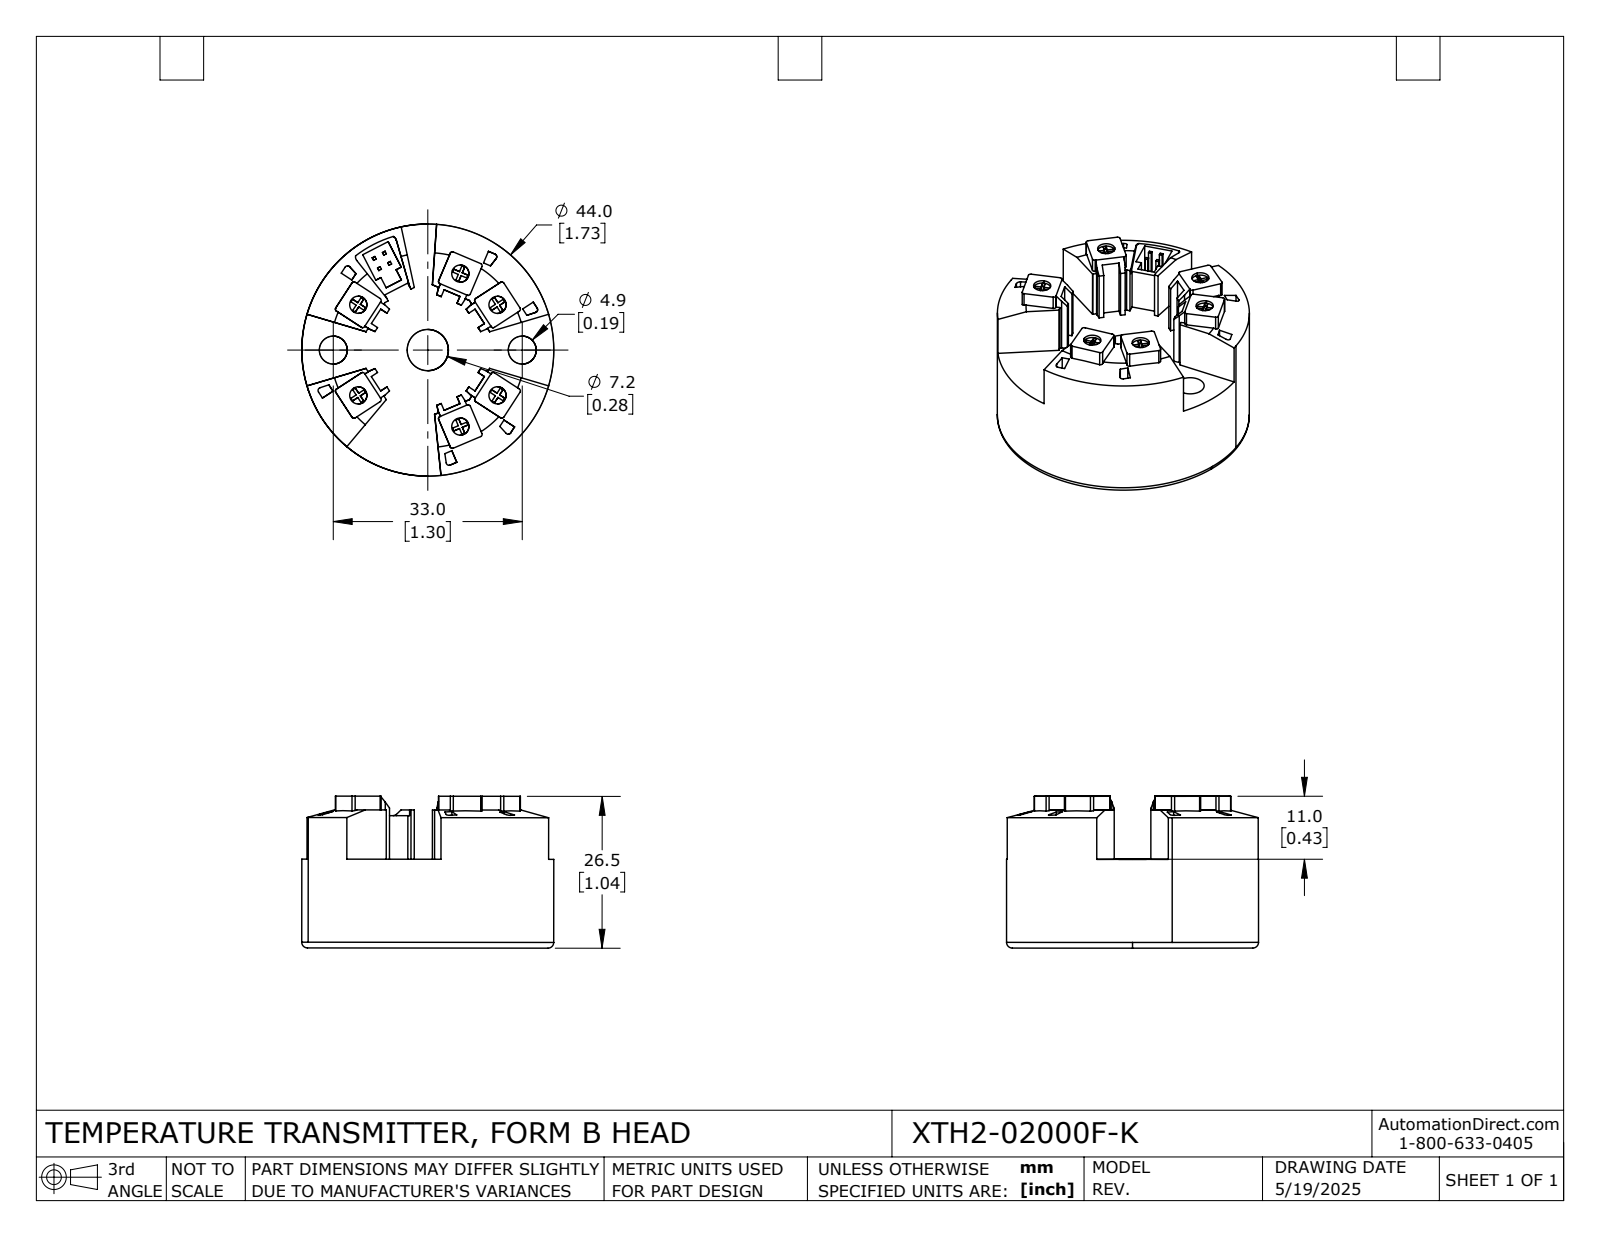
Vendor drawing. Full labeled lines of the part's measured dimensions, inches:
Part name (STEP PRODUCT): XTDH2-02000F-K
STEP written by: SolidWorks 2024 (AUTOMOTIVE_DESIGN)
Units: inches
Bodies: 1 solid, 341 faces (281 planar, 52 cylindrical, 8 other)
Overall size (bounding box): 1.733 × 1.732 × 1.045
Volume: 1.748 in³ · Surface area: 13.46 in²
Round holes (diameter × count): ⌀0.118 ×6, ⌀0.193 ×2, ⌀0.283 ×1
Round bosses / shafts (diameter × count): ⌀1.732 ×1
Partial cylindrical surfaces — rounded edges, fillets, slot ends (radius × count): R0.016 ×24, R0.02 ×6, R0.039 ×2
Main face-to-face distances: 0.61, 1.043, 0.433, 0.059, 0.177, 0.039, 0.02, 0.118, 0.949, 0.339
Hole centre spacings: 0.571, 0.333, 0.355, 0.356, 0.65, 0.677, 0.733, 0.875
